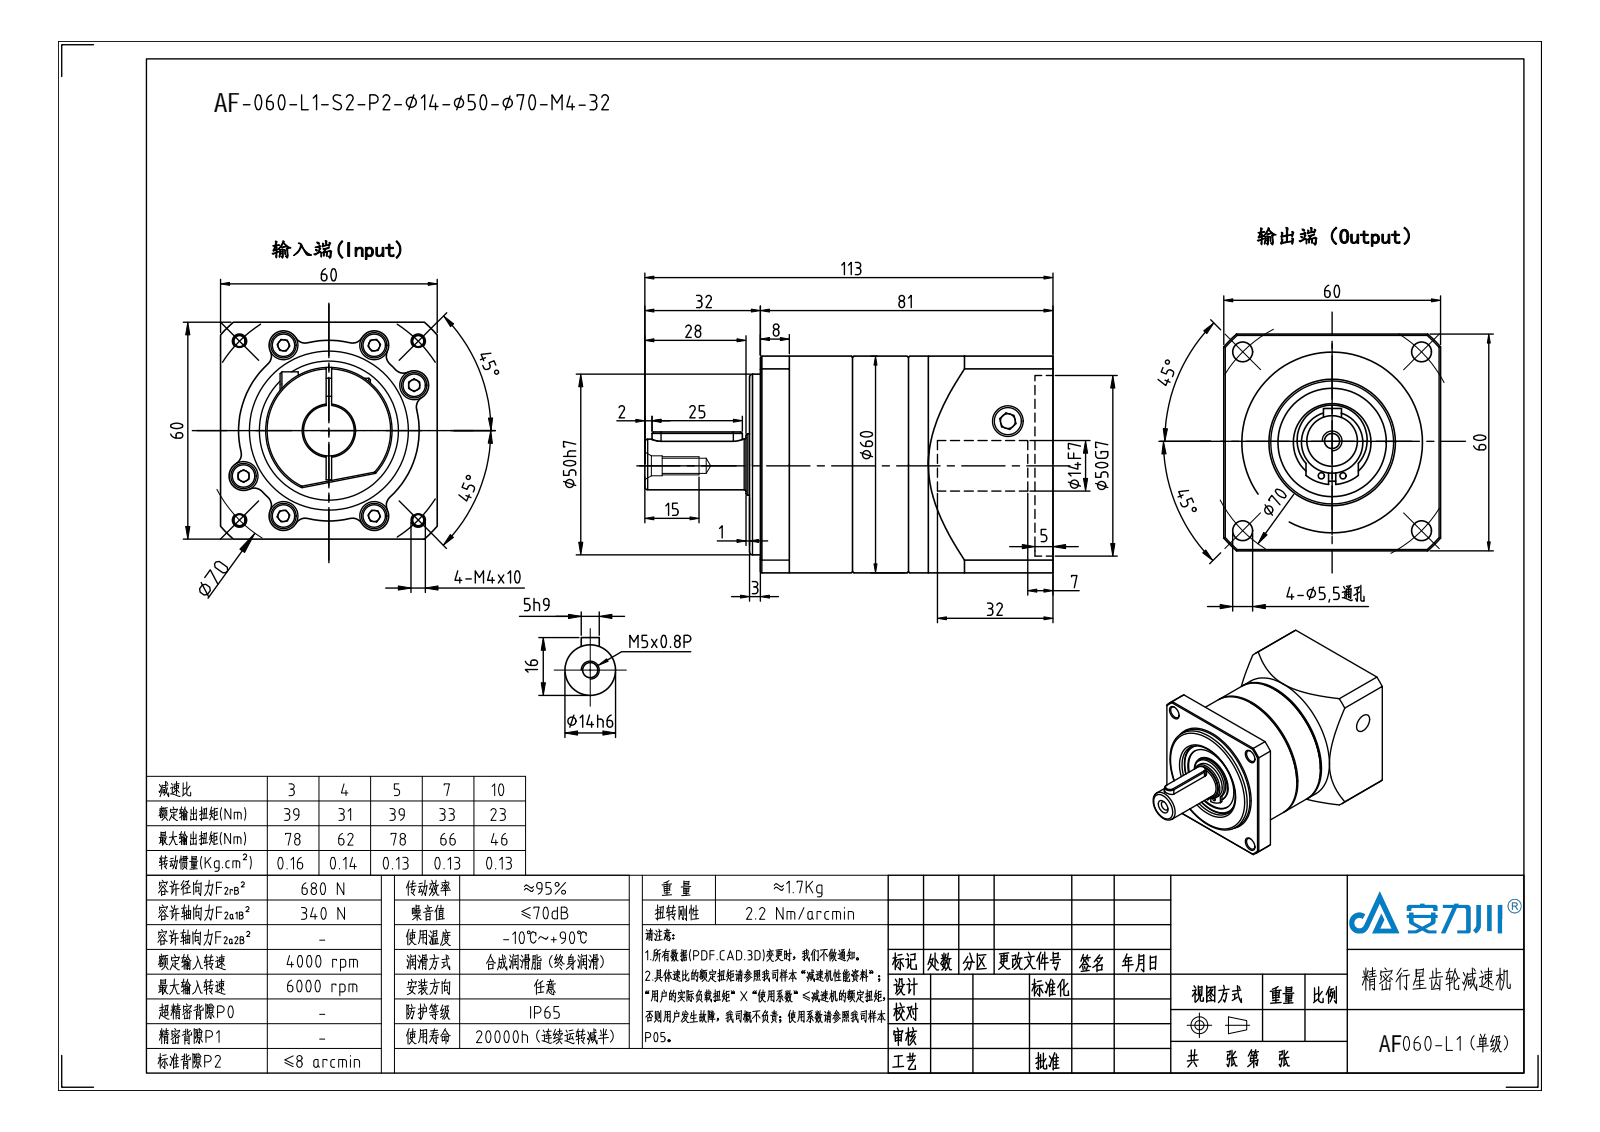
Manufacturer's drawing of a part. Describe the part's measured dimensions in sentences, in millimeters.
The part is named "输出行星架PG060; 内齿圈PG060-D108; 输出轴卡簧17; 输入法兰PG060-50 (+6 more)". Its 3-D file was written by "SolidWorks 2018 (CONFIG_CONTROL_DESIGN)". It is 14 solids with 530 faces: 191 planar, 195 cylindrical and 144 other. Overall it measures 113 by 60 by 60 millimeters. Its volume is 194 400 cubic millimeters and its surface area 64 561 square millimeters. Round holes: 10 of diameter 3.3, 6 of diameter 4.5, 6 of diameter 8, 4 of diameter 5.5, 2 of diameter 1.7, 2 of diameter 4.3, 1 of diameter 8.5, 1 of diameter 14, 1 of diameter 14.5, 1 of diameter 15.7, 1 of diameter 30, 1 of diameter 35. Round bosses or shafts: 6 of diameter 7, 6 of diameter 4, 1 of diameter 60, 1 of diameter 47, 1 of diameter 24.5, 1 of diameter 21.5, 1 of diameter 20, 1 of diameter 17. Partial cylindrical surfaces (rounded edges, fillets, slot ends): 12 of radius 3, 2 of radius 0.5, 2 of radius 2.5, 1 of radius 4.5, 1 of radius 9.7, 1 of radius 11.65, 1 of radius 40. The main face-to-face distances are 15.5, 60, 3, 1.5, 41, 20, 25.5, 33, 40, 55.5. The hole center spacings are 12.24, 26.75, 37.33, 49.88, 61.09, 35, 37.83, 49.5.
